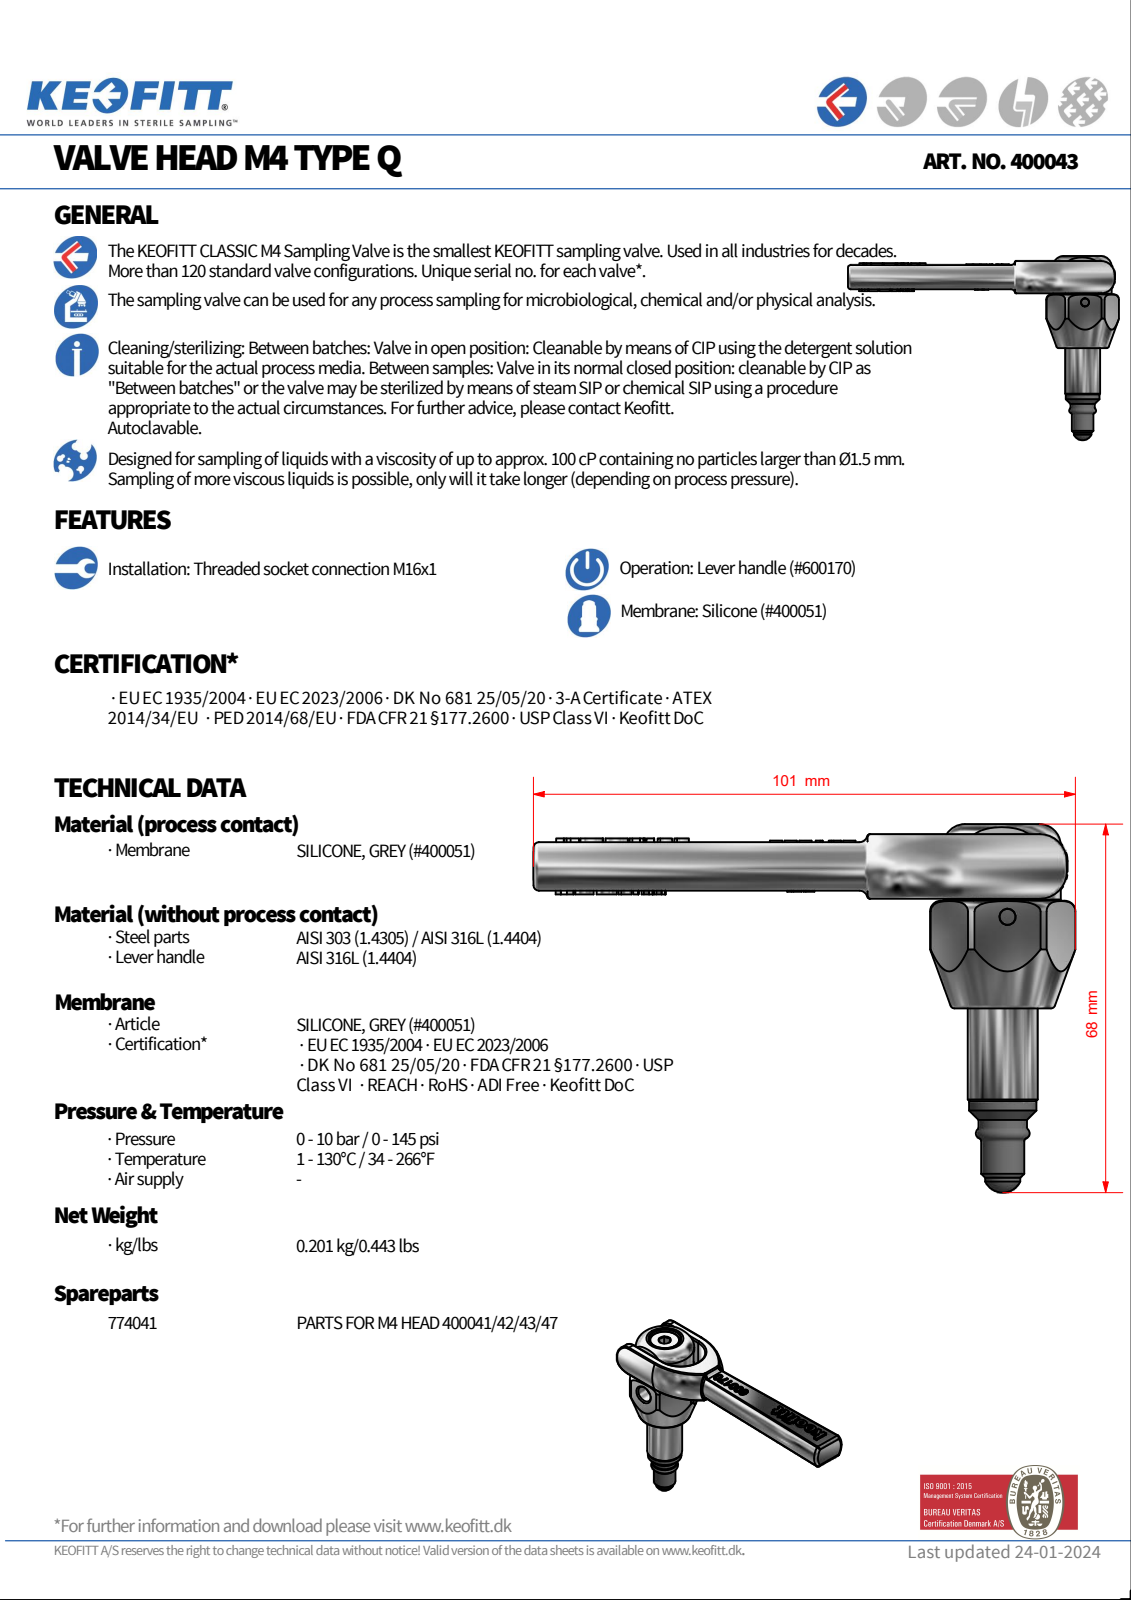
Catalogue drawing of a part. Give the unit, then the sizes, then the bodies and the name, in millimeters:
Units: millimetres
Overall size (bounding box): 100.21 × 69.2 × 48.8
Round holes (diameter × count): ⌀3.05 ×1, ⌀6.1 ×1, ⌀10.2 ×1, ⌀16.5 ×1
Round bosses / shafts (diameter × count): ⌀13 ×1, ⌀12.5 ×1, ⌀10 ×1, ⌀9 ×1, ⌀8 ×1, ⌀6.5 ×1, ⌀3 ×1
Partial cylindrical surfaces — rounded edges, fillets, slot ends (radius × count): R0.5 ×14, R1 ×2, R1.5 ×2, R3 ×2, R5 ×2, R1.75 ×1, R9.1 ×1, R11 ×1
Main face-to-face distances: 1.5, 9, 1, 10.5, 24, 11.5, 2.5, 2, 12, 0.5
Hole centre spacings: 2
Volume: 27 385 mm³ · Surface area: 9 989 mm²
Bodies: 1 solid, 517 faces (208 planar, 48 cylindrical, 261 other)
STEP written by: Autodesk Inventor 2008 (AUTOMOTIVE_DESIGN)
